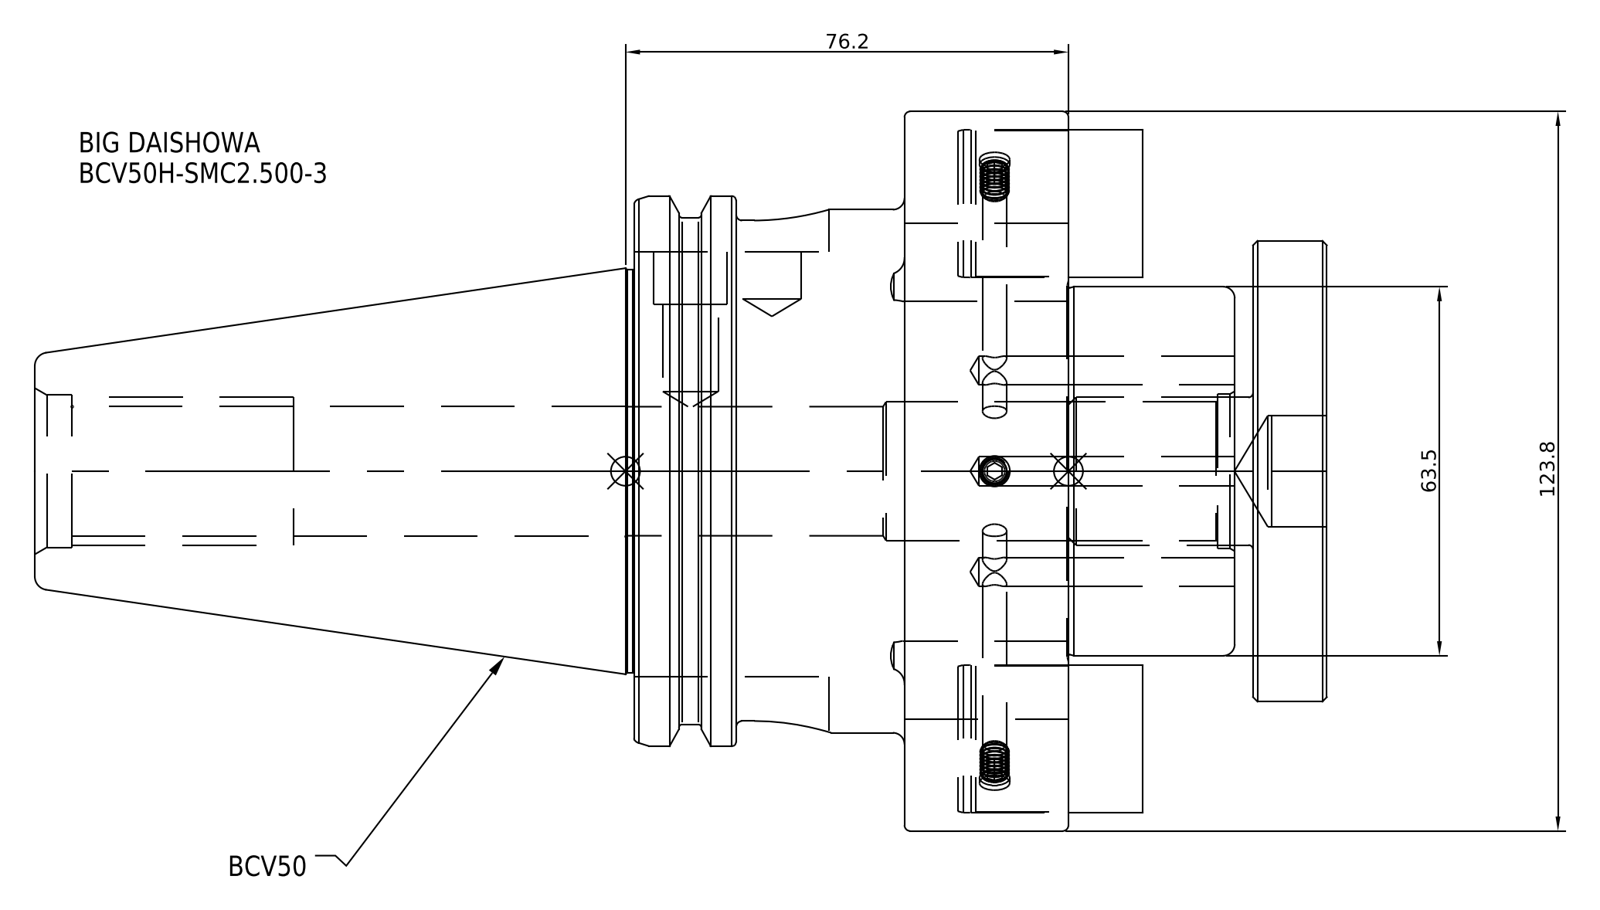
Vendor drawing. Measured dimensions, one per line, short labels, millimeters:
name: BCV50H-SMC2_500-3
written by: SolidWorks 2021 (CONFIG_CONTROL_DESIGN)
unit: mm
bodies: 1 solid, 38 faces (18 planar, 14 cylindrical, 6 other)
size: 190.5 × 123.8 × 123.8
volume: 908 760 mm³; area: 72 666 mm²
holes: 1× ⌀23.81
bosses: 1× ⌀123.8, 1× ⌀98.43, 1× ⌀91.29, 1× ⌀90, 1× ⌀69.85
face distances: 28.19, 74.7, 46.51, 25.4, 12.7, 40.89, 87.4, 190.5, 177.8, 149.61
